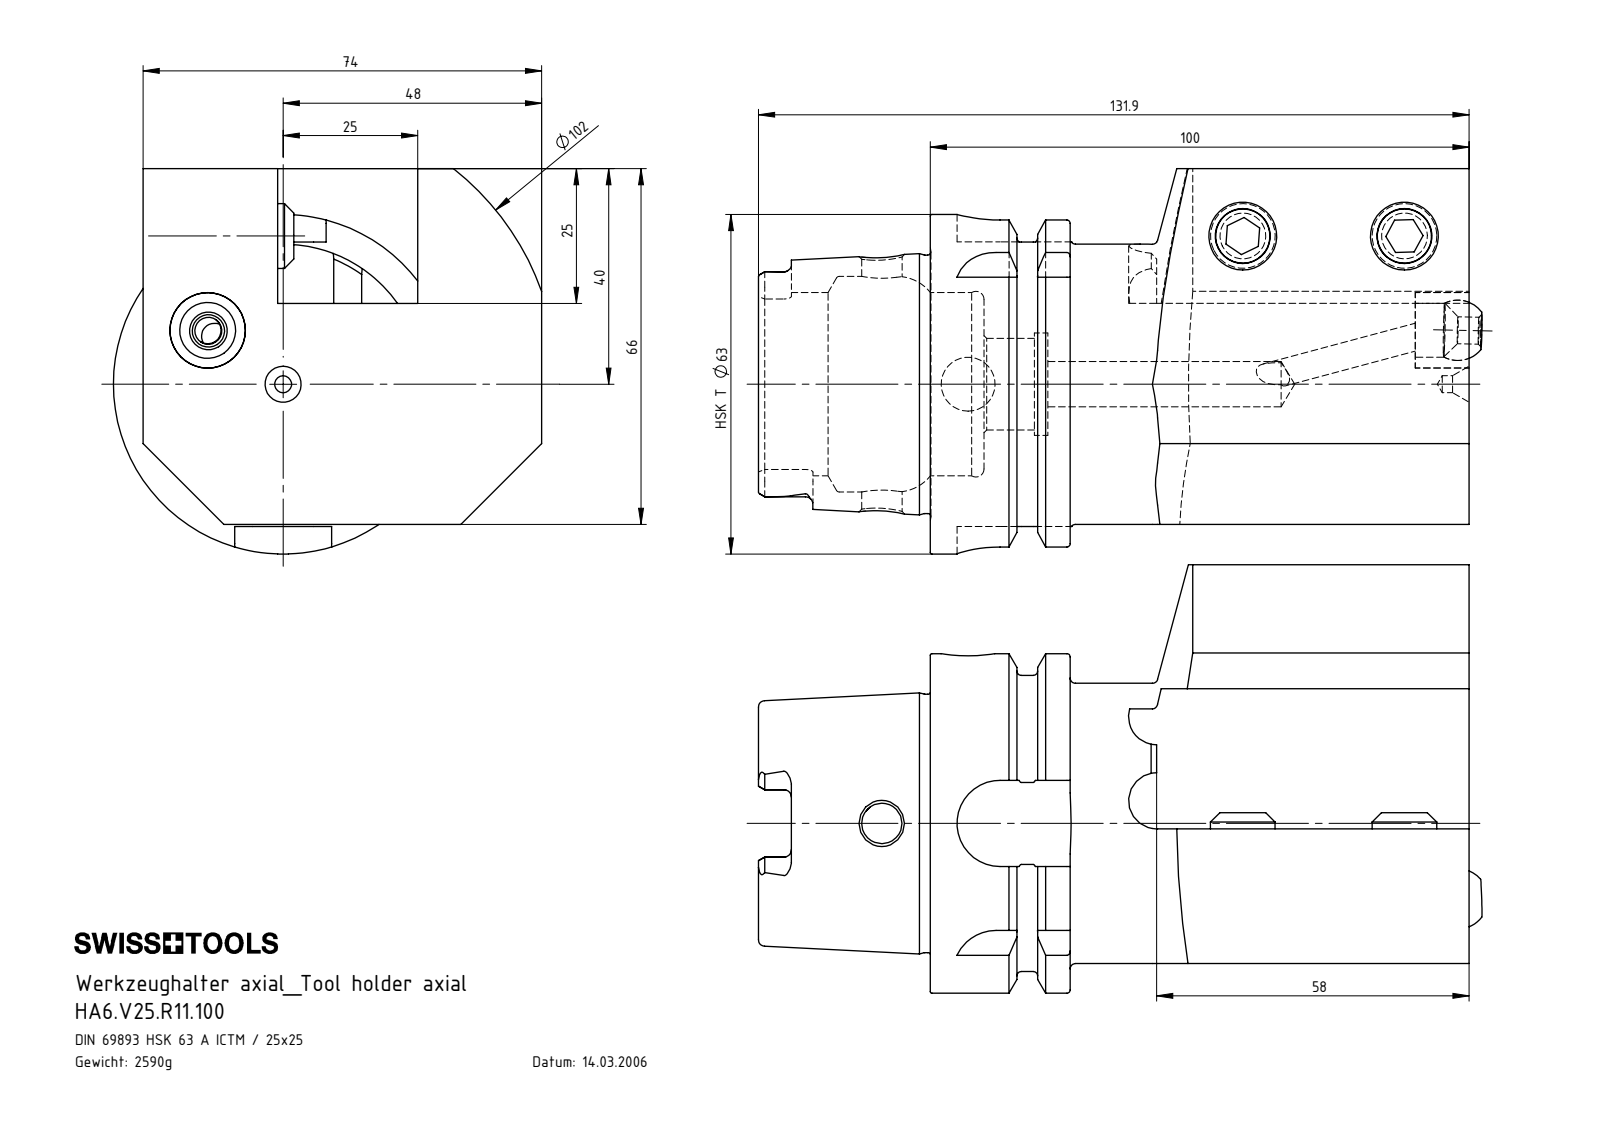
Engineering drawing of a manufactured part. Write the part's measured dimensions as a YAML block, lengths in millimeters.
part_name: "KU1-U14.001.012_2; HA6-V25.R11.100_B; KU1-U14.001.012; ISO 4026 - M12 x 25 (+2 more)"
step_written_by: "SolidWorks 2017 (AUTOMOTIVE_DESIGN)"
units: millimeters
bodies: {solids: 5, faces: 243, planar: 76, cylindrical: 70, other: 97}
overall_size: [134.71, 79.5, 71.5]
volume: 330516
surface_area: 52432
round_holes:
  - {diameter: 5, count: 2}
  - {diameter: 10, count: 2}
  - {diameter: 10.2, count: 2}
  - {diameter: 3.15, count: 1}
  - {diameter: 7.5, count: 1}
  - {diameter: 8.4, count: 1}
  - {diameter: 14, count: 1}
  - {diameter: 17, count: 1}
  - {diameter: 19, count: 1}
  - {diameter: 34, count: 1}
  - {diameter: 40, count: 1}
round_bosses_or_shafts:
  - {diameter: 12, count: 2}
  - {diameter: 63, count: 1}
  - {diameter: 54.95, count: 1}
  - {diameter: 52, count: 1}
  - {diameter: 47.94, count: 1}
partial_cylinders:
  - {radius: 1.4, count: 6}
  - {radius: 2.88, count: 4}
  - {radius: 8, count: 4}
  - {radius: 5.2, count: 2}
  - {radius: 51, count: 1}
face_to_face_distances: [25, 66, 41, 23, 74, 51, 49, 26, 100, 16]
hole_center_spacings: [17.2, 30, 57.94, 85.54]
